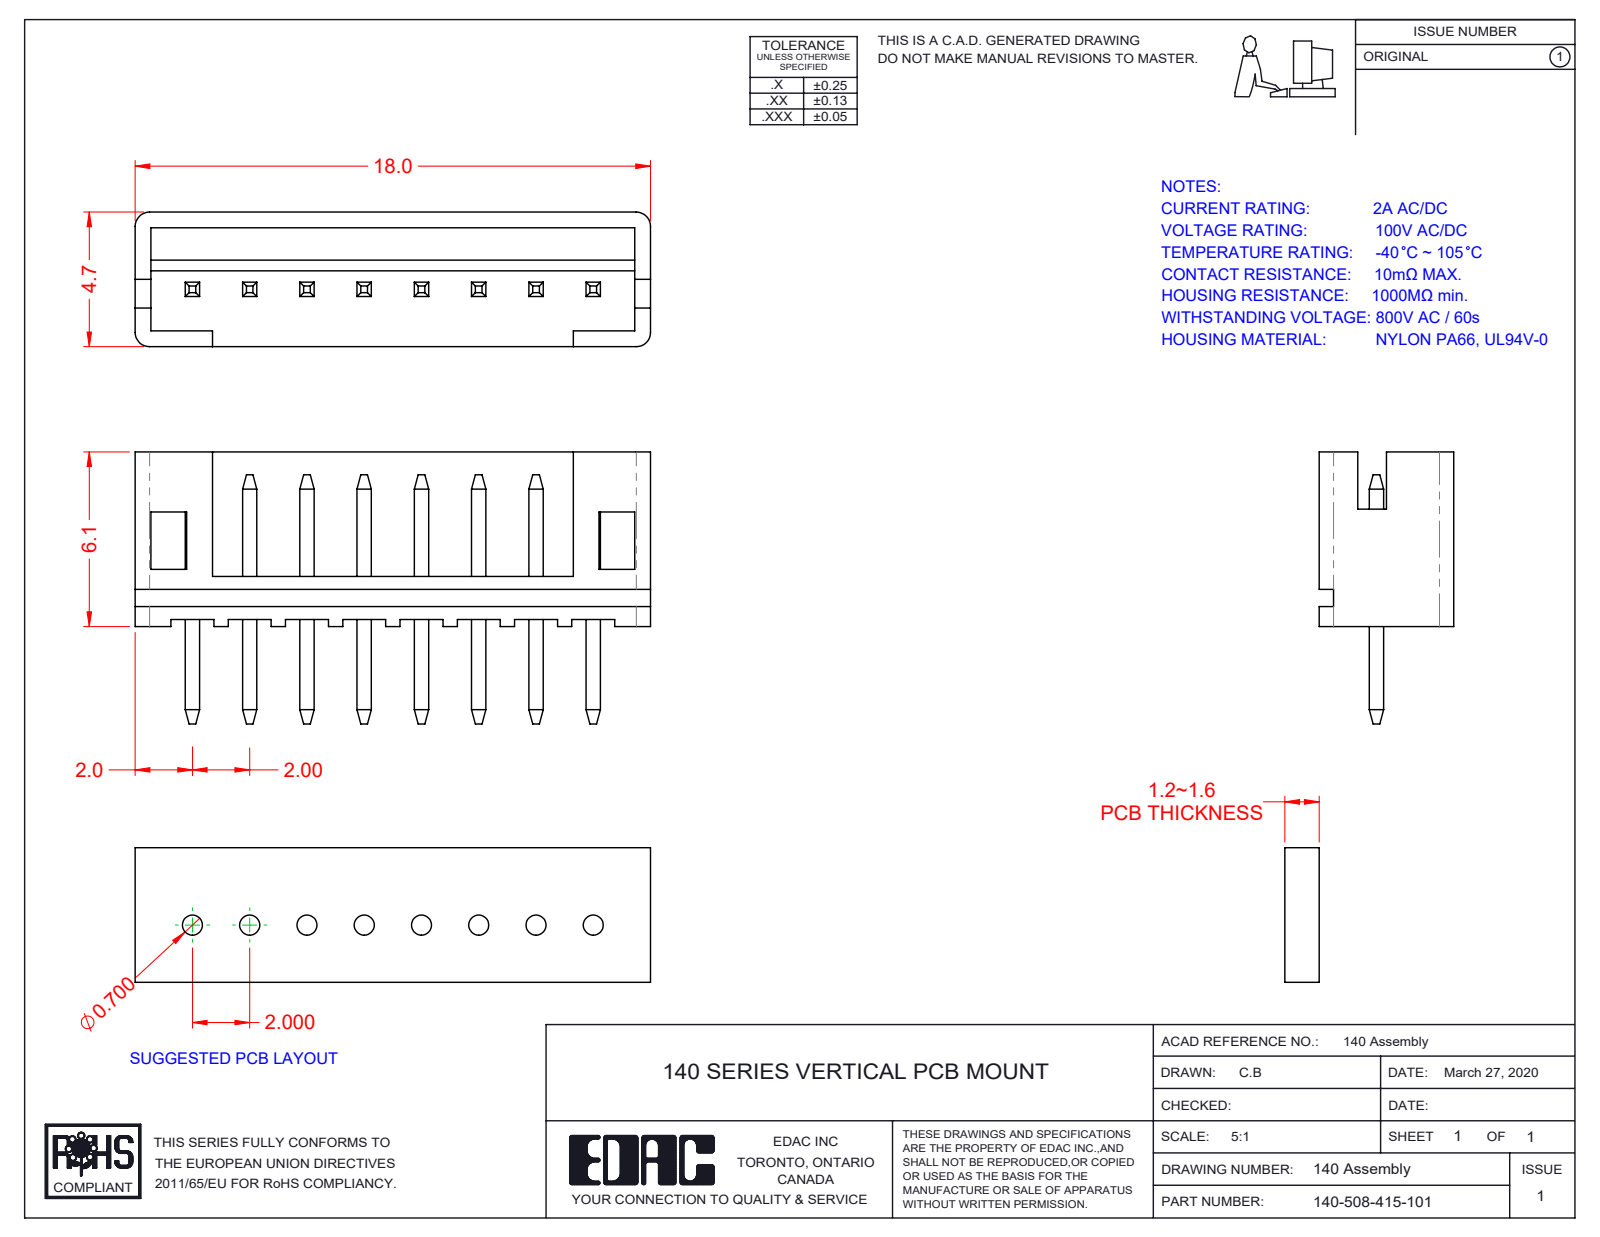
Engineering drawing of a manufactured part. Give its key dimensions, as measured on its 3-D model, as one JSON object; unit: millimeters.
{"part_name": "V LI Housing_508; V LI Contact_Str; 140-508-415-101", "step_written_by": "SolidWorks 2020 (CONFIG_CONTROL_DESIGN)", "units": "millimeters", "bodies": {"solids": 9, "faces": 216, "planar": 210, "cylindrical": 6, "other": 0}, "overall_size": [18, 9.5, 4.7], "volume_mm3": 195, "surface_area_mm2": 713, "partial_cylinders_radius": [[0.5, 4]], "face_to_face_distances": [0.55, 0.5, 1.75, 1.5, 2, 4, 6, 4.15, 2.25, 2.45]}
